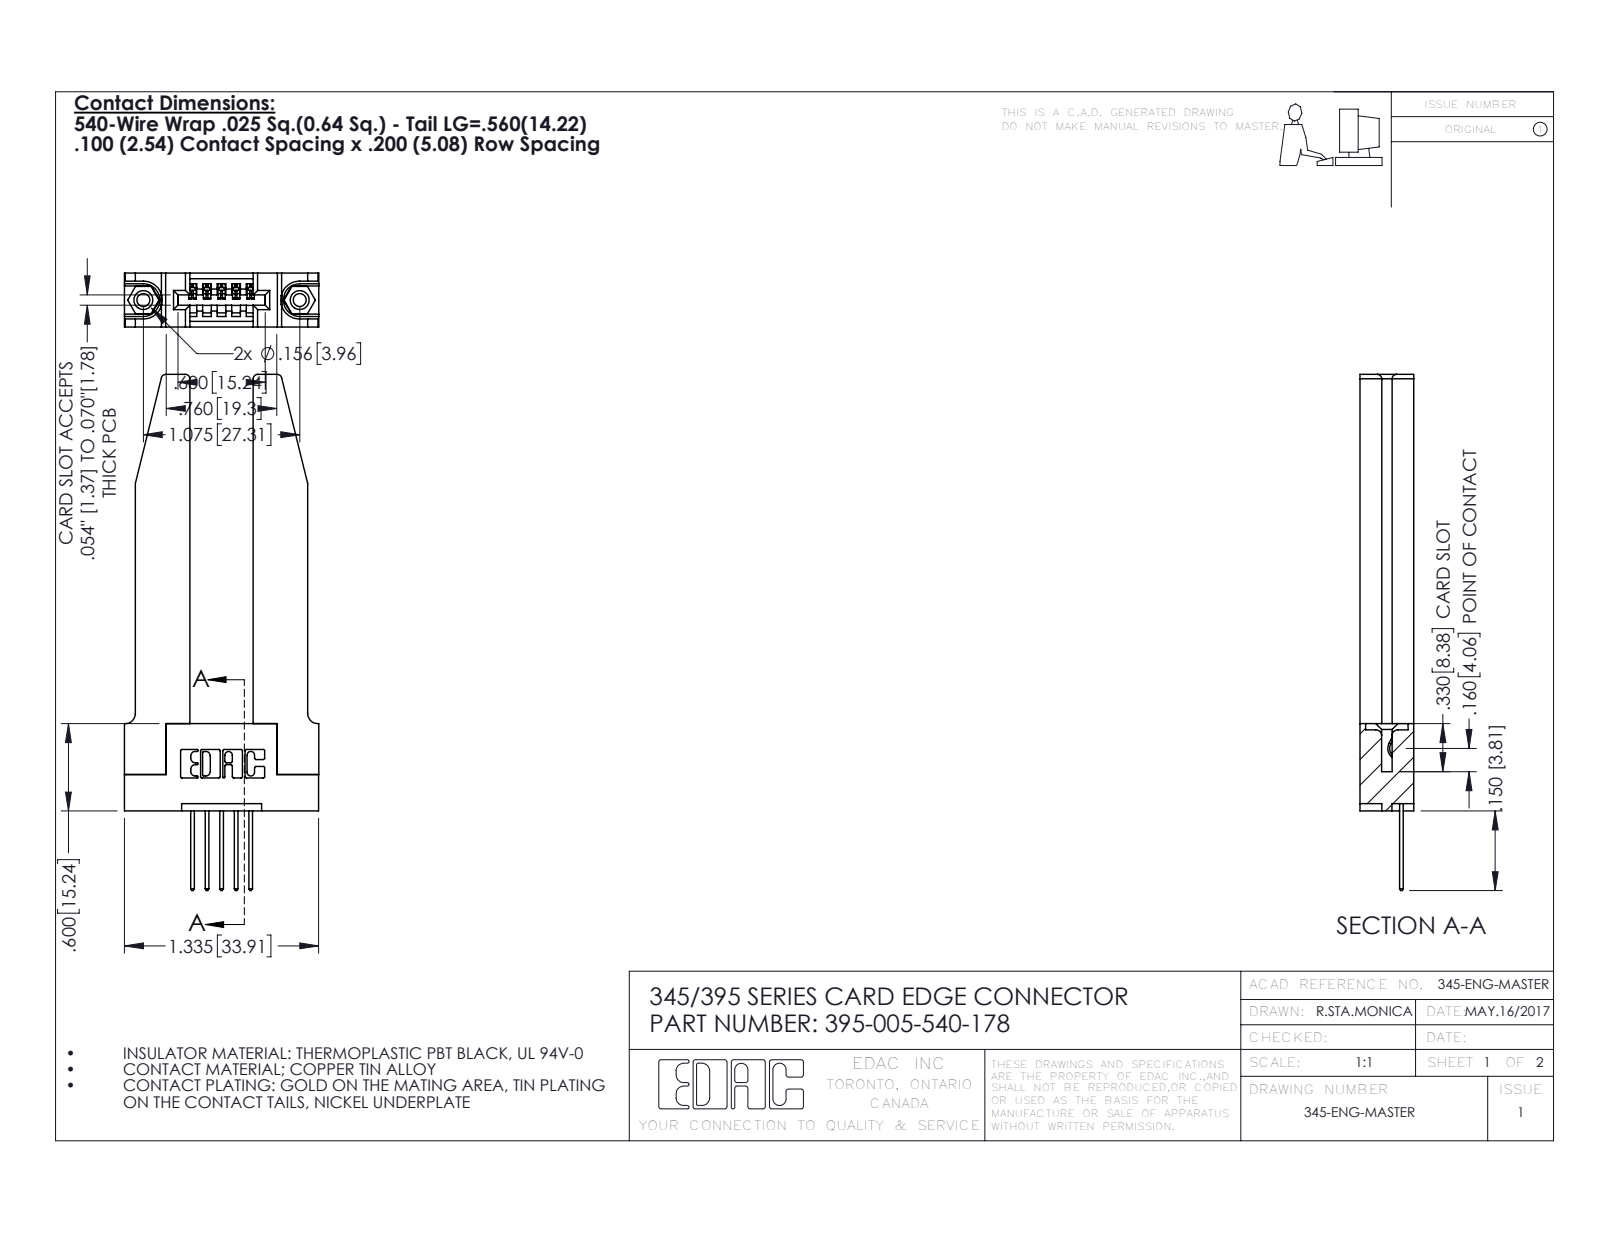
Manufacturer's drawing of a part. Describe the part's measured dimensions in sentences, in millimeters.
The part is named "395-005-540-178; 345-220-078_345-220-078; 345-250-001_345-250-001-102; 345-292-001_345-293-140 (+1 more)". Its 3-D file was written by "SolidWorks 2016 (CONFIG_CONTROL_DESIGN)". It is 10 solids with 650 faces: 422 planar, 176 cylindrical and 52 other. Overall it measures 90.1 by 33.9 by 9.4 millimeters. Its volume is 10 700 cubic millimeters and its surface area 10 280 square millimeters. Round holes: 2 of diameter 2.3, 2 of diameter 3.2, 2 of diameter 4, 1 of diameter 1.6. Round bosses or shafts: 2 of diameter 3.9. Partial cylindrical surfaces (rounded edges, fillets, slot ends): 22 of radius 0.3, 10 of radius 0.2, 10 of radius 0.3, 8 of radius 0.8, 6 of radius 0.2, 6 of radius 0.8, 3 of radius 0.7, 2 of radius 0.8. The main face-to-face distances are 9.4, 3.8, 5.6, 11, 3.8, 1.8, 5.1, 2, 7.6, 2.4. The hole center spacings are 6.9, 21.5, 27.3.
